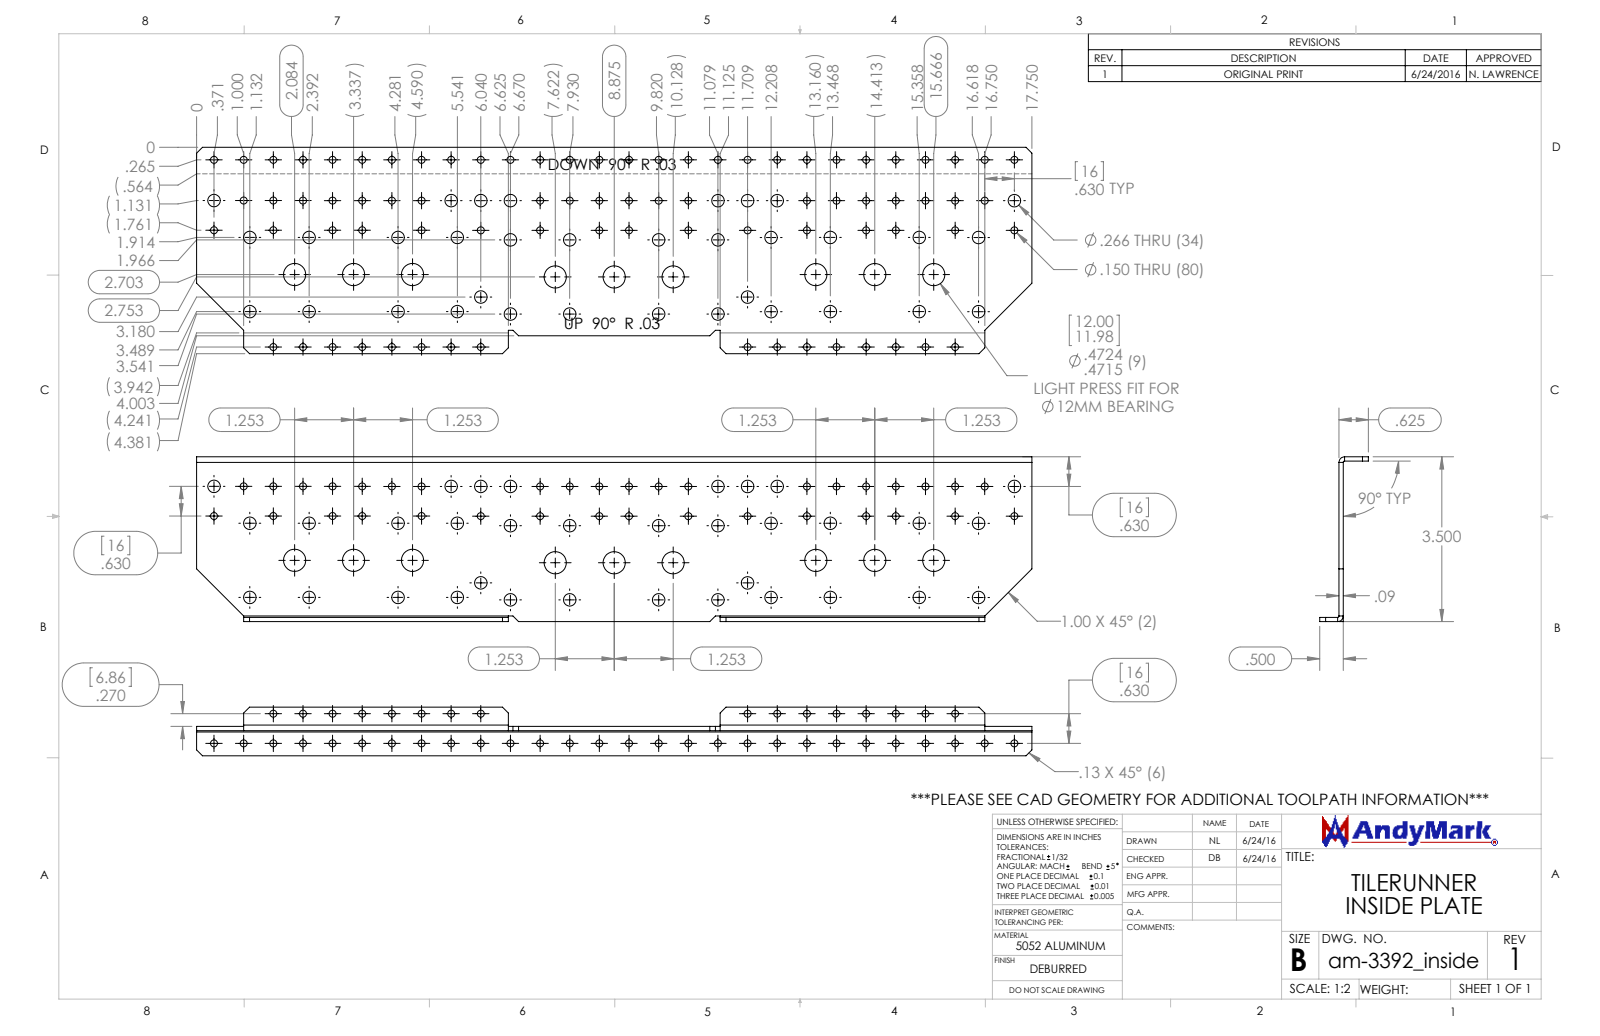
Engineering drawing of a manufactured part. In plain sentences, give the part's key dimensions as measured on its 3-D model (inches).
The part is named "am-3392_Inside TileRunner Inside Plate". Its 3-D file was written by "SolidWorks 2021 (AUTOMOTIVE_DESIGN)". It is 1 solid with 290 faces: 38 planar, 252 cylindrical and 0 other. Overall it measures 17.75 by 3.5 by 1.035 inches. Its volume is 6.22 cubic inches and its surface area 149.3 square inches. Round holes: 80 of diameter 0.15, 34 of diameter 0.266, 9 of diameter 0.472. Partial cylindrical surfaces (rounded edges, fillets, slot ends): 2 of radius 0.029, 2 of radius 0.119. The main face-to-face distances are 0.09, 3.41, 3.5, 0.09, 3.32, 3.41, 0.535, 0.625, 1.035, 0.5. The hole center spacings are 0.63, 1.26, 1.89, 2.52, 3.15, 3.78, 4.409, 0.891.
